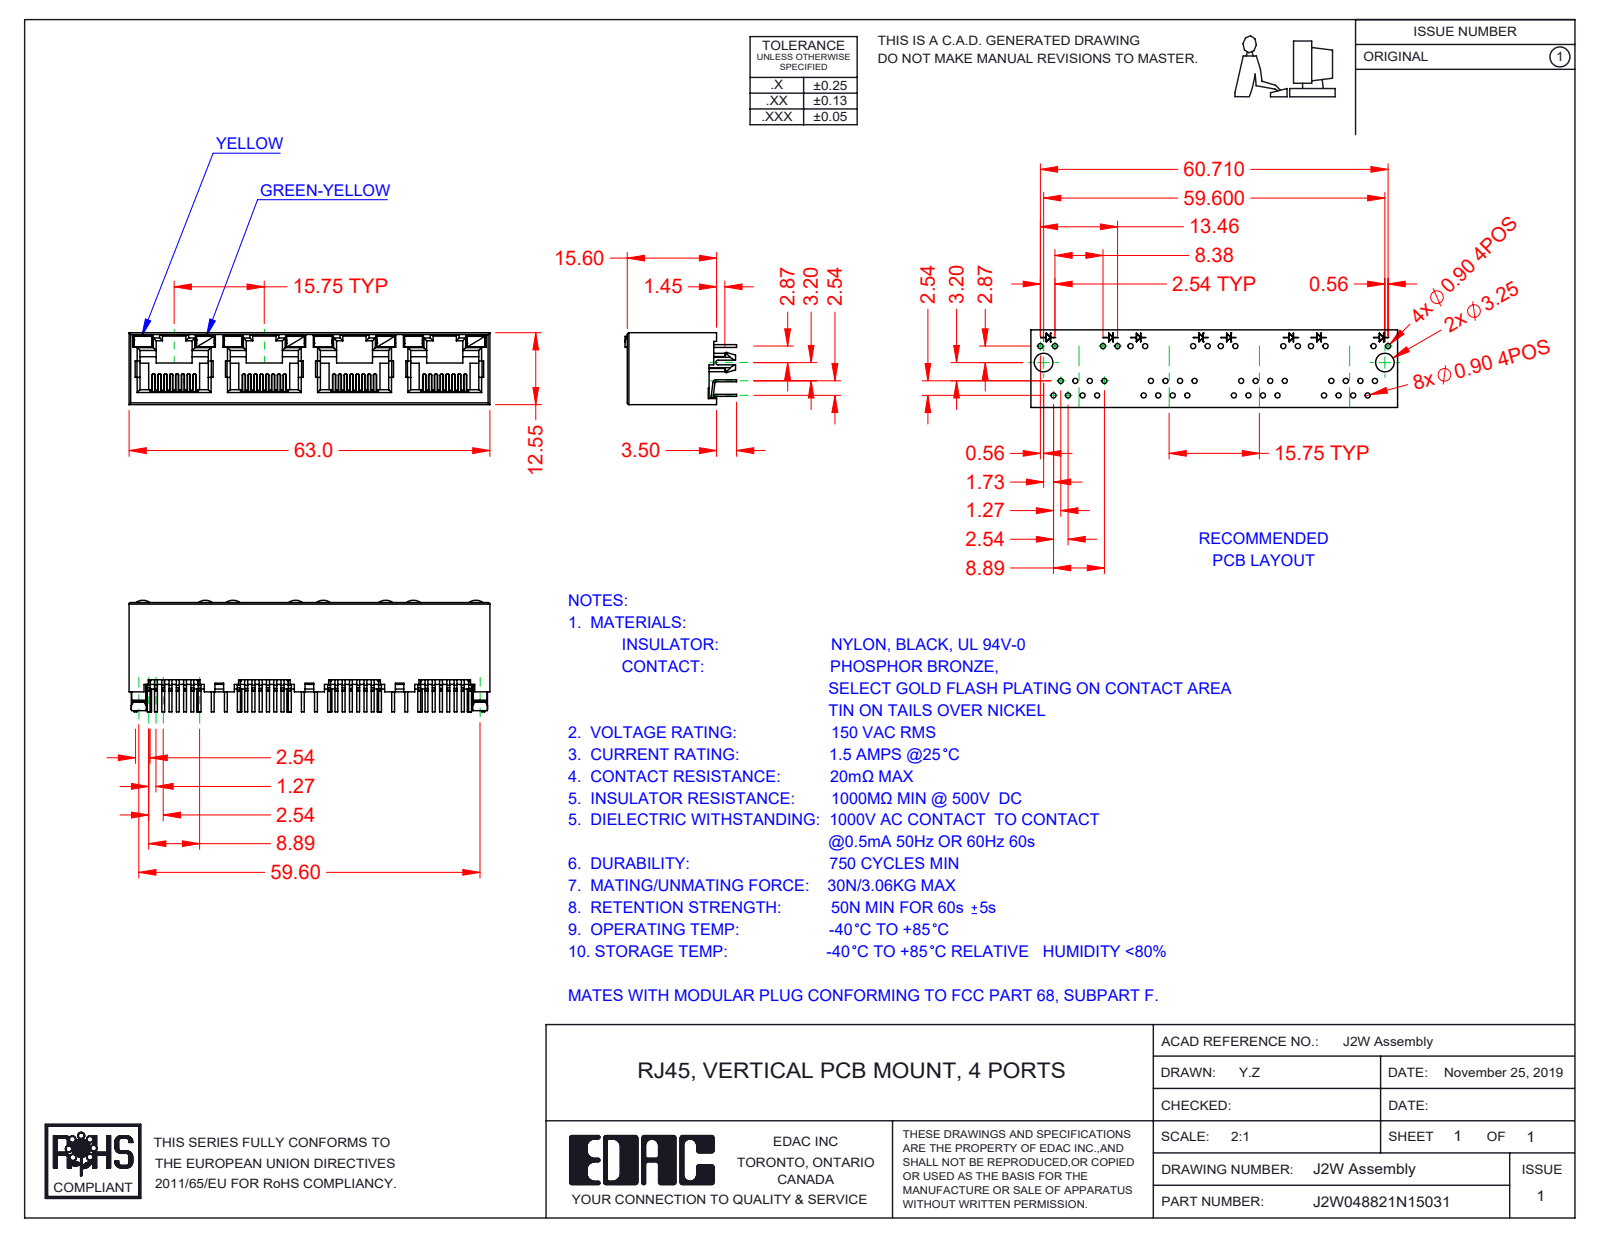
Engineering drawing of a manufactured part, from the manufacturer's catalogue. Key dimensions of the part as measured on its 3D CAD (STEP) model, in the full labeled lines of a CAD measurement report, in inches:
Part name (STEP PRODUCT): 2W Insulator; J2W048821N15031; 2W Contact Lock; 2W Contacts (+2 more)
STEP written by: SolidWorks 2020 (CONFIG_CONTROL_DESIGN)
Units: inches
Bodies: 45 solids, 3139 faces (2600 planar, 481 cylindrical, 58 other)
Overall size (bounding box): 2.48 × 0.768 × 0.494
Volume: 0.326 in³ · Surface area: 20.37 in²
Partial cylindrical surfaces — rounded edges, fillets, slot ends (radius × count): R0.006 ×64, R0.008 ×29, R0.02 ×28, R0.012 ×14, R0.018 ×8, R0.079 ×8, R0.01 ×2, R0.059 ×2
Main face-to-face distances: 0.494, 0.469, 0.026, 0.62, 0.014, 0.059, 0.031, 0.024, 0.445, 1.24
